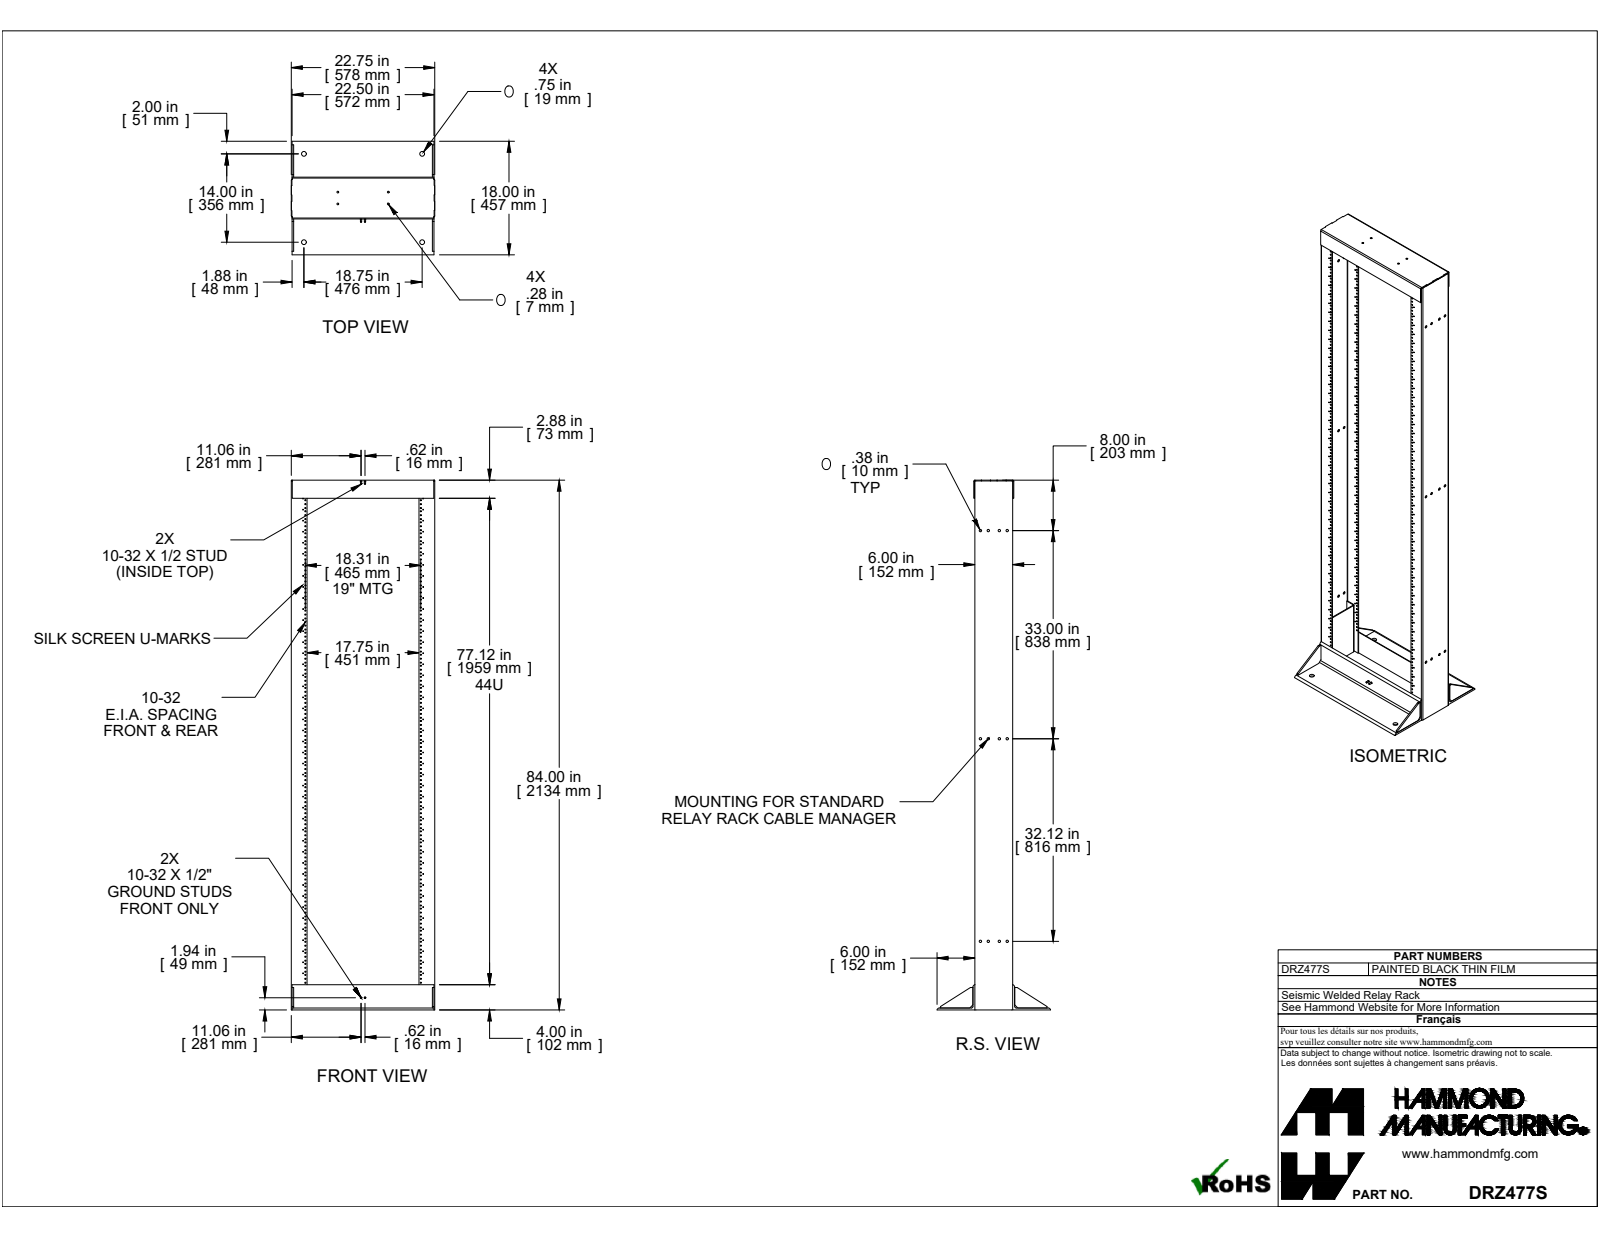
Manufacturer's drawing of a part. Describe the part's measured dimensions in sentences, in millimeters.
The part is named "DRZ477S". Its 3-D file was written by "SolidWorks 2019 (CONFIG_CONTROL_DESIGN)". It is 15 solids with 936 faces: 138 planar, 794 cylindrical and 4 other. Overall it measures 2133.6 by 577.9 by 457.2 millimeters. Its volume is 6 825 000 cubic millimeters and its surface area 3 532 000 square millimeters. Round holes: 274 of diameter 4.5, 90 of diameter 3.2, 16 of diameter 9.5, 4 of diameter 7.1, 4 of diameter 19.1. Round bosses or shafts: 4 of diameter 6.4, 4 of diameter 4.8. Partial cylindrical surfaces (rounded edges, fillets, slot ends): 4 of radius 1.2, 4 of radius 2.5, 4 of radius 4.4, 4 of radius 5.7, 2 of radius 1.5, 2 of radius 4.7, 2 of radius 6.4, 2 of radius 9.8. The main face-to-face distances are 3.2, 3.2, 571.5, 574.7, 574.7, 577.9, 152.4, 149.2, 149.2, 146.1. The hole center spacings are 44.5, 88.9, 31.8, 76.2, 133.4, 177.8, 222.3, 266.7.
